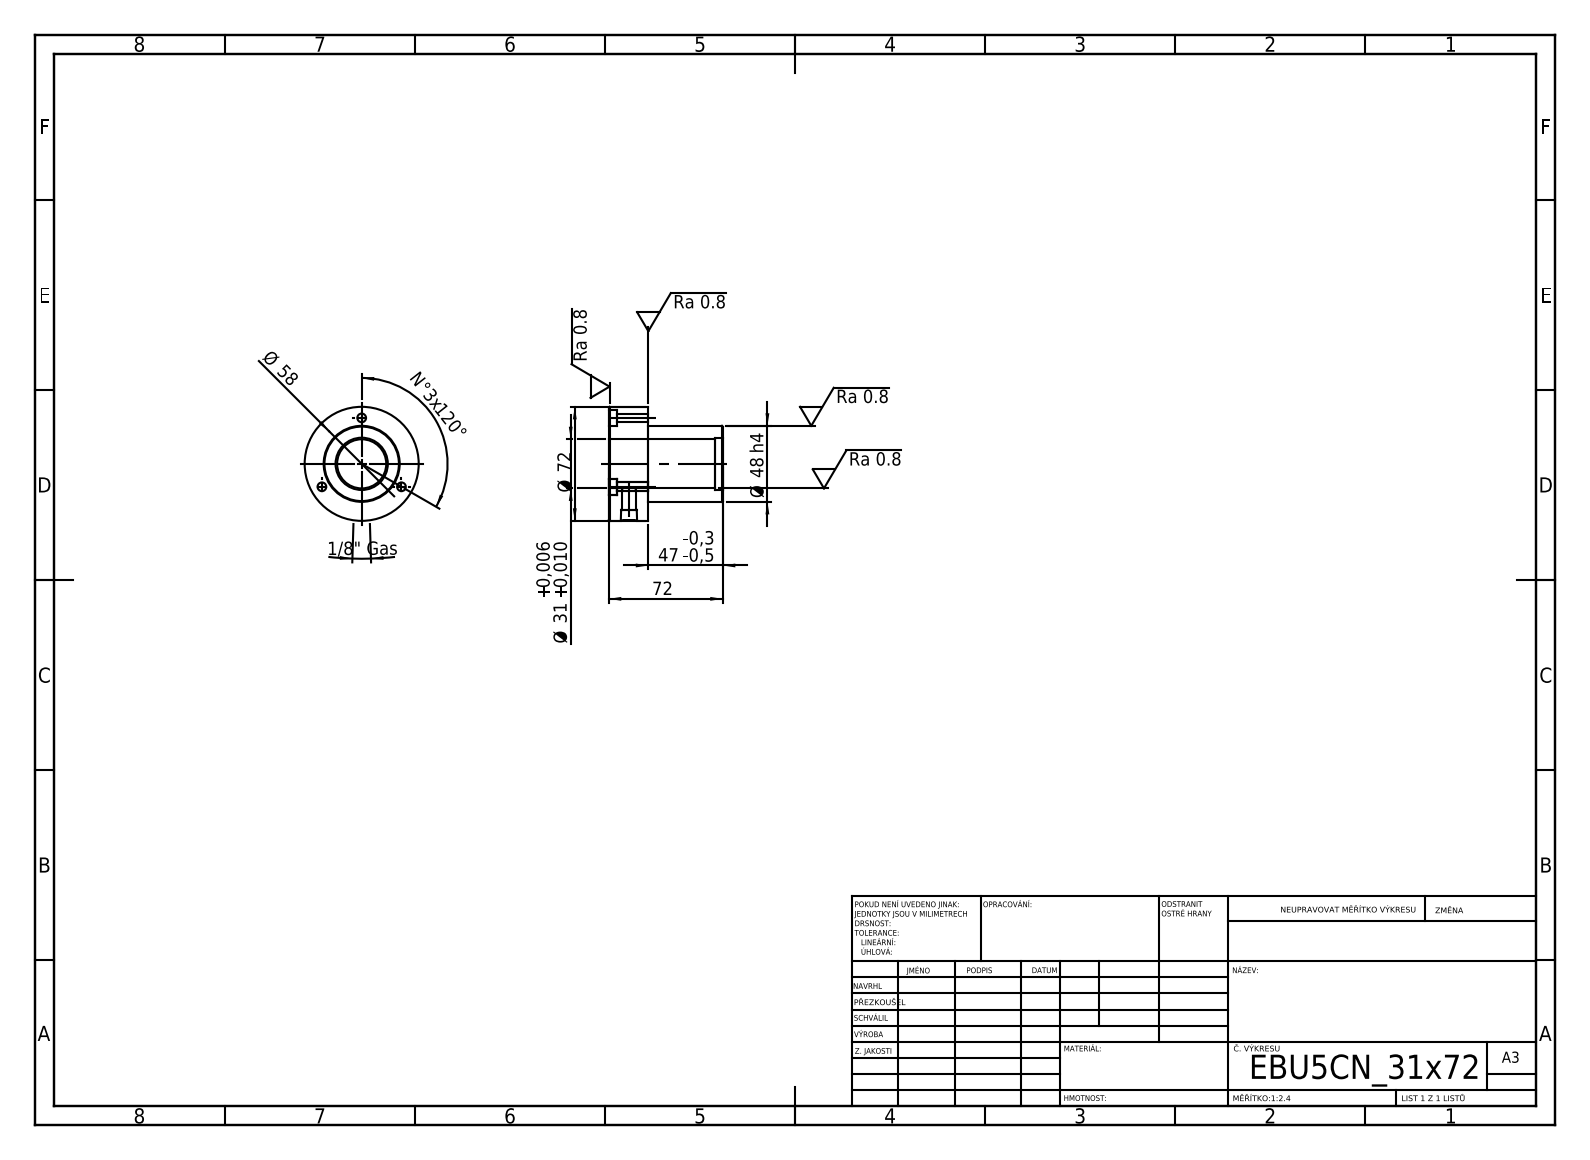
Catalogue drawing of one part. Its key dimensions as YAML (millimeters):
step_written_by: "SolidWorks 2019 (CONFIG_CONTROL_DESIGN)"
units: millimeters
bodies: {solids: 1, faces: 36, planar: 8, cylindrical: 22, other: 6}
overall_size: [72, 72, 72]
volume: 127963
surface_area: 28152
round_holes:
  - {diameter: 5.5, count: 3}
  - {diameter: 10, count: 3}
  - {diameter: 8.43, count: 1}
  - {diameter: 31, count: 1}
  - {diameter: 33, count: 1}
round_bosses_or_shafts:
  - {diameter: 72, count: 1}
  - {diameter: 48, count: 1}
face_to_face_distances: [25, 47, 72, 66.6, 19.6, 5.4, 5, 42, 61.6, 67]
hole_center_spacings: [29, 50.23, 50.22]
